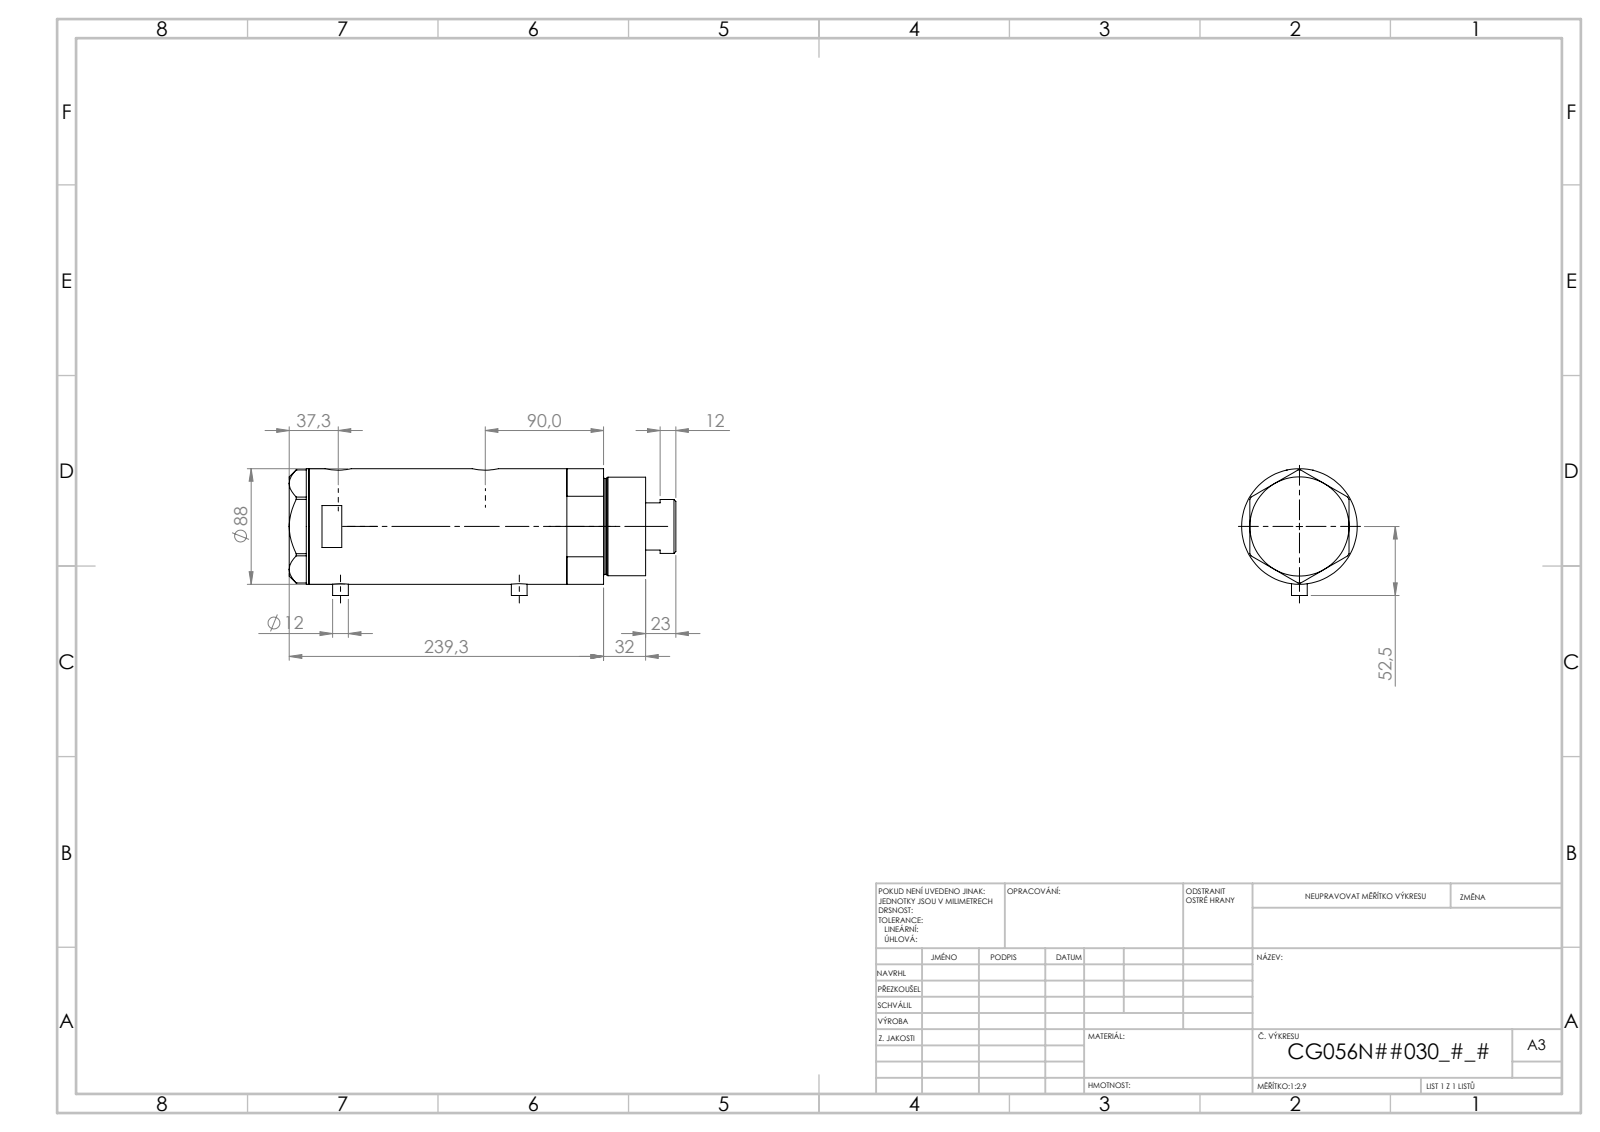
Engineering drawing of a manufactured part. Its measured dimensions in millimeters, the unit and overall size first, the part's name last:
Units: millimetres
Overall size (bounding box): 254.47 × 89.1 × 88
Round holes (diameter × count): ⌀5 ×2, ⌀12.5 ×2, ⌀13.16 ×2, ⌀20 ×2, ⌀14.5 ×1, ⌀42 ×1, ⌀43.5 ×1, ⌀56 ×1, ⌀60 ×1, ⌀80 ×1
Round bosses / shafts (diameter × count): ⌀12 ×2, ⌀88 ×1, ⌀75 ×1, ⌀73 ×1, ⌀41 ×1
Main face-to-face distances: 104.4, 26, 78.4, 15, 41, 119.4, 216.47, 231.47, 190.47, 112.07
Hole centre spacings: 1.7, 25.8, 80.3, 82, 106.1, 107.8
Volume: 1 312 000 mm³ · Surface area: 197 790 mm²
Bodies: 4 solids, 126 faces (53 planar, 53 cylindrical, 20 other)
Part name (STEP PRODUCT): V270CG_BACK; V270CG_FRONT; V270CG_VC; V270CG_MIDDLE
STEP written by: SolidWorks 2019 (CONFIG_CONTROL_DESIGN)
